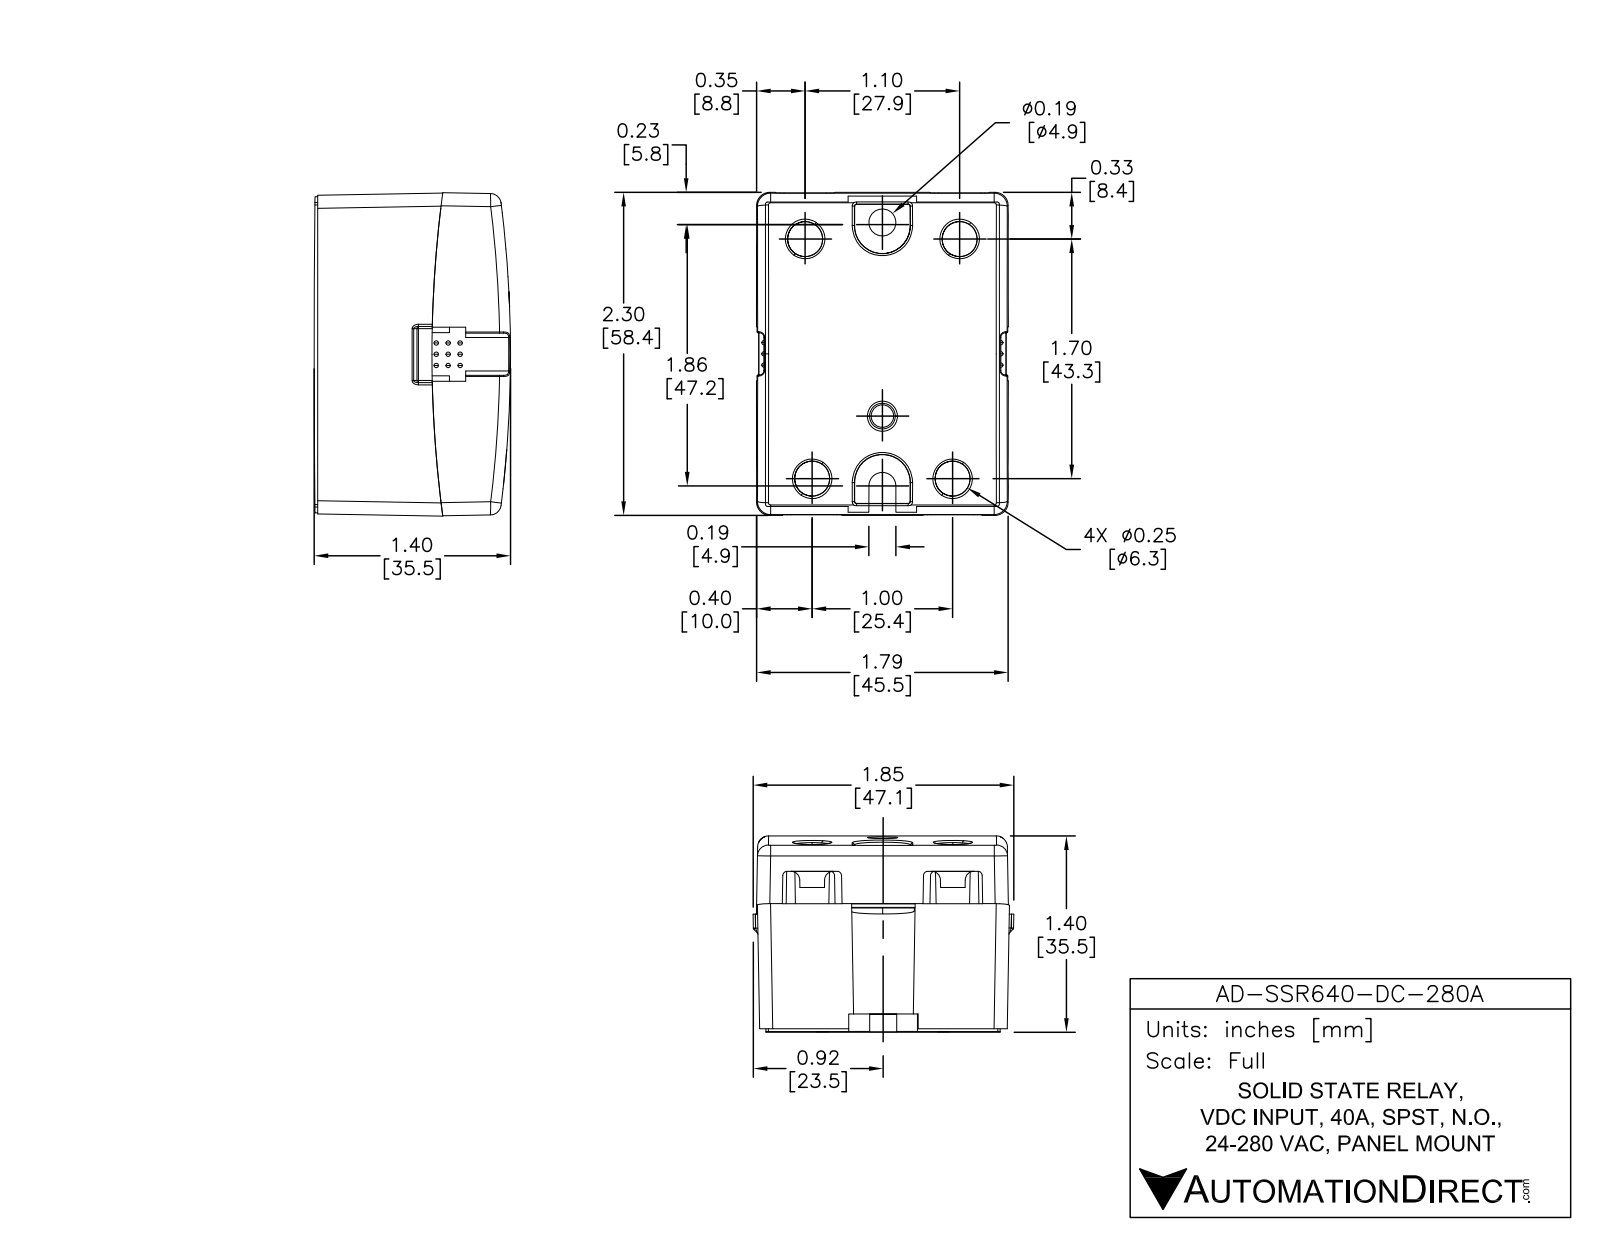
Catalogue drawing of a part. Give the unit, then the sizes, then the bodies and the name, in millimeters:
Units: millimetres
Overall size (bounding box): 58.4 × 45.5 × 35.6
Round holes (diameter × count): ⌀6.4 ×4, ⌀4.8 ×1
Round bosses / shafts (diameter × count): ⌀10.2 ×2, ⌀8.9 ×2, ⌀7.6 ×2, ⌀6.4 ×2, ⌀5.1 ×2, ⌀5.1 ×2
Partial cylindrical surfaces — rounded edges, fillets, slot ends (radius × count): R0.8 ×6, R0.3 ×4, R1 ×4, R12.7 ×4, R4.9 ×2, R2.4 ×1, R12.7 ×1, R12.7 ×1
Main face-to-face distances: 45.5, 58.4, 29.6, 6.4, 23.3, 17, 26.9, 12.7, 45.7, 2
Hole centre spacings: 14.1, 14.4, 25.4, 27.9, 43.2, 43.2, 47.7, 47.7
Volume: 84 230 mm³ · Surface area: 17 040 mm²
Bodies: 3 solids, 251 faces (145 planar, 95 cylindrical, 11 other)
Part name (STEP PRODUCT): AD-SSR640-DC-280A
STEP written by: SolidWorks 2013 (AUTOMOTIVE_DESIGN)
